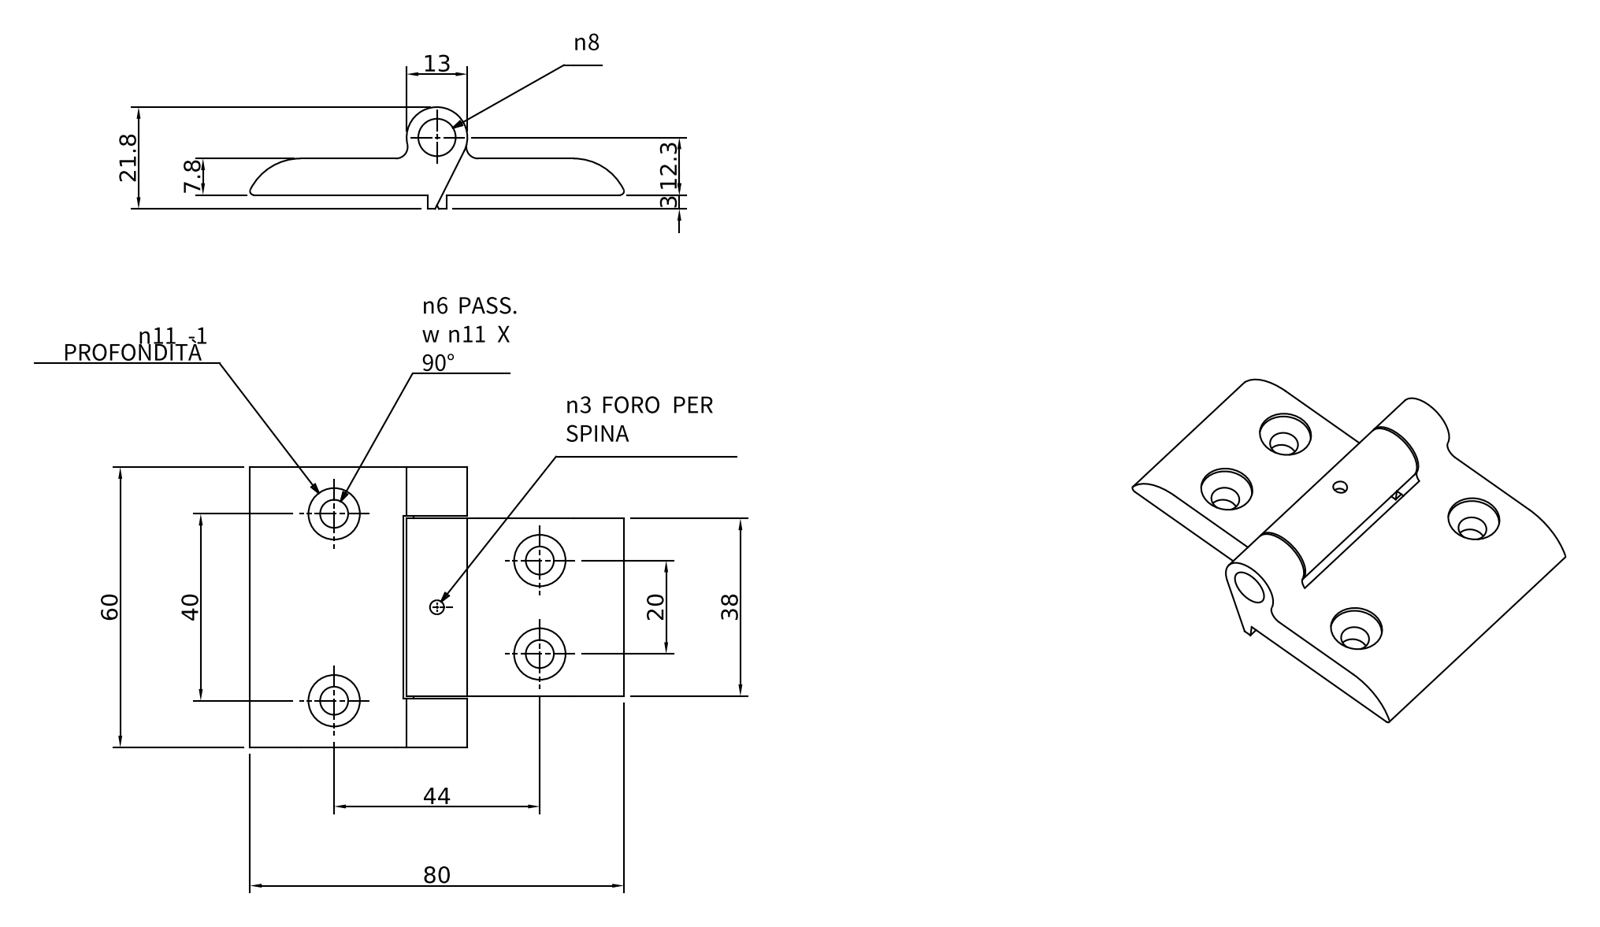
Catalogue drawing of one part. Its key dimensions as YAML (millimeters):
part_name: "CCRYY0000018; 440000016425; 440000016426"
step_written_by: "Autodesk Inventor 2019 (AUTOMOTIVE_DESIGN)"
units: millimeters
bodies: {solids: 2, faces: 46, planar: 20, cylindrical: 20, other: 6}
overall_size: [80, 60, 21.8]
volume: 31272
surface_area: 14009
round_holes:
  - {diameter: 6, count: 4}
  - {diameter: 11, count: 4}
  - {diameter: 3, count: 1}
  - {diameter: 8, count: 1}
partial_cylinders:
  - {radius: 2.5, count: 2}
  - {radius: 12, count: 2}
  - {radius: 6.5, count: 1}
face_to_face_distances: [7.8, 11, 49, 38, 60, 10.5, 49.5, 0.5, 38.5, 39]
hole_center_spacings: [24.17, 29.73, 45.12, 53.25, 20, 40]
